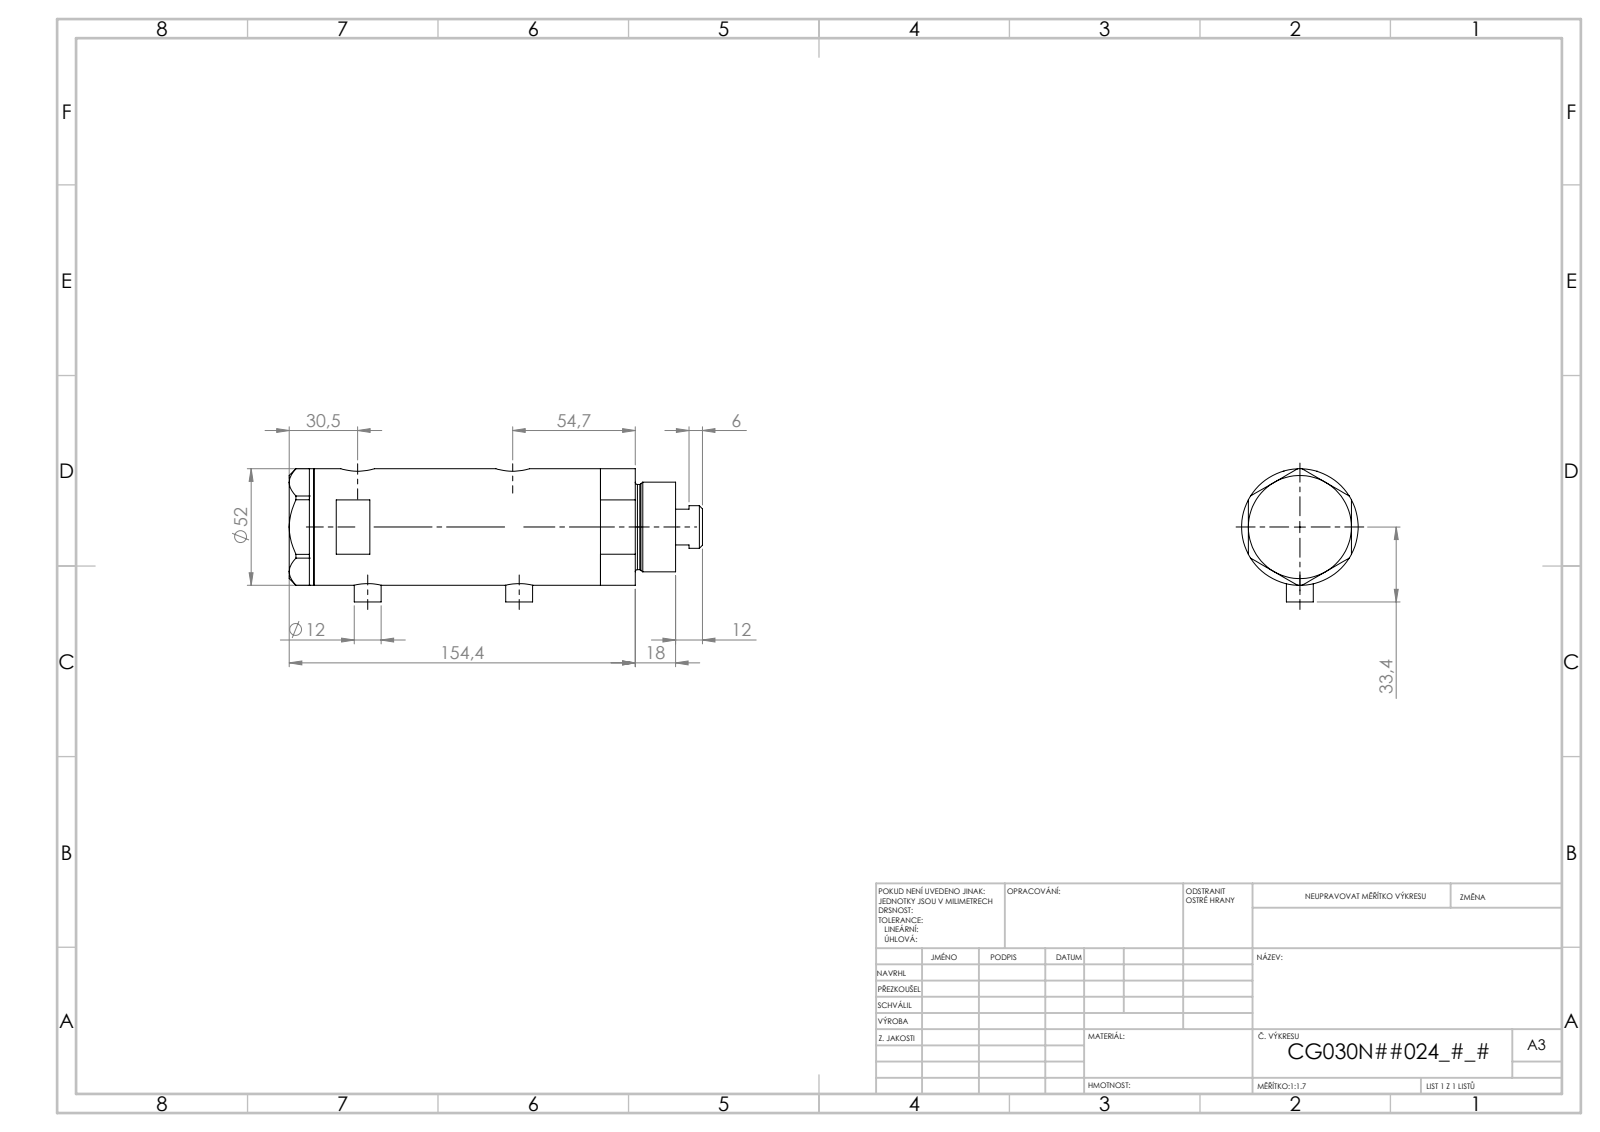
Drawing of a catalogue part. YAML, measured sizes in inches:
part_name: "V270CG_VC; V270CG_MIDDLE; V270CG_BACK; V270CG_FRONT"
step_written_by: "SolidWorks 2019 (CONFIG_CONTROL_DESIGN)"
units: inches
bodies: {solids: 4, faces: 140, planar: 67, cylindrical: 53, other: 20}
overall_size: [6.812, 2.091, 2.047]
volume: 18.86
surface_area: 112.8
round_holes:
  - {diameter: 0.197, count: 2}
  - {diameter: 0.383, count: 2}
  - {diameter: 0.492, count: 2}
  - {diameter: 0.591, count: 2}
  - {diameter: 0.256, count: 1}
  - {diameter: 0.787, count: 1}
  - {diameter: 0.846, count: 1}
  - {diameter: 1.181, count: 1}
  - {diameter: 1.299, count: 1}
  - {diameter: 1.732, count: 1}
round_bosses_or_shafts:
  - {diameter: 0.472, count: 2}
  - {diameter: 2.047, count: 1}
  - {diameter: 1.575, count: 1}
  - {diameter: 1.496, count: 1}
  - {diameter: 0.748, count: 1}
face_to_face_distances: [3.054, 0.937, 2.117, 0.433, 1.37, 3.487, 1.811, 4.92, 4.487, 3.55]
hole_center_spacings: [0.114, 0.177, 1.998, 2.112, 2.175, 2.289, 0.114, 0.115]
